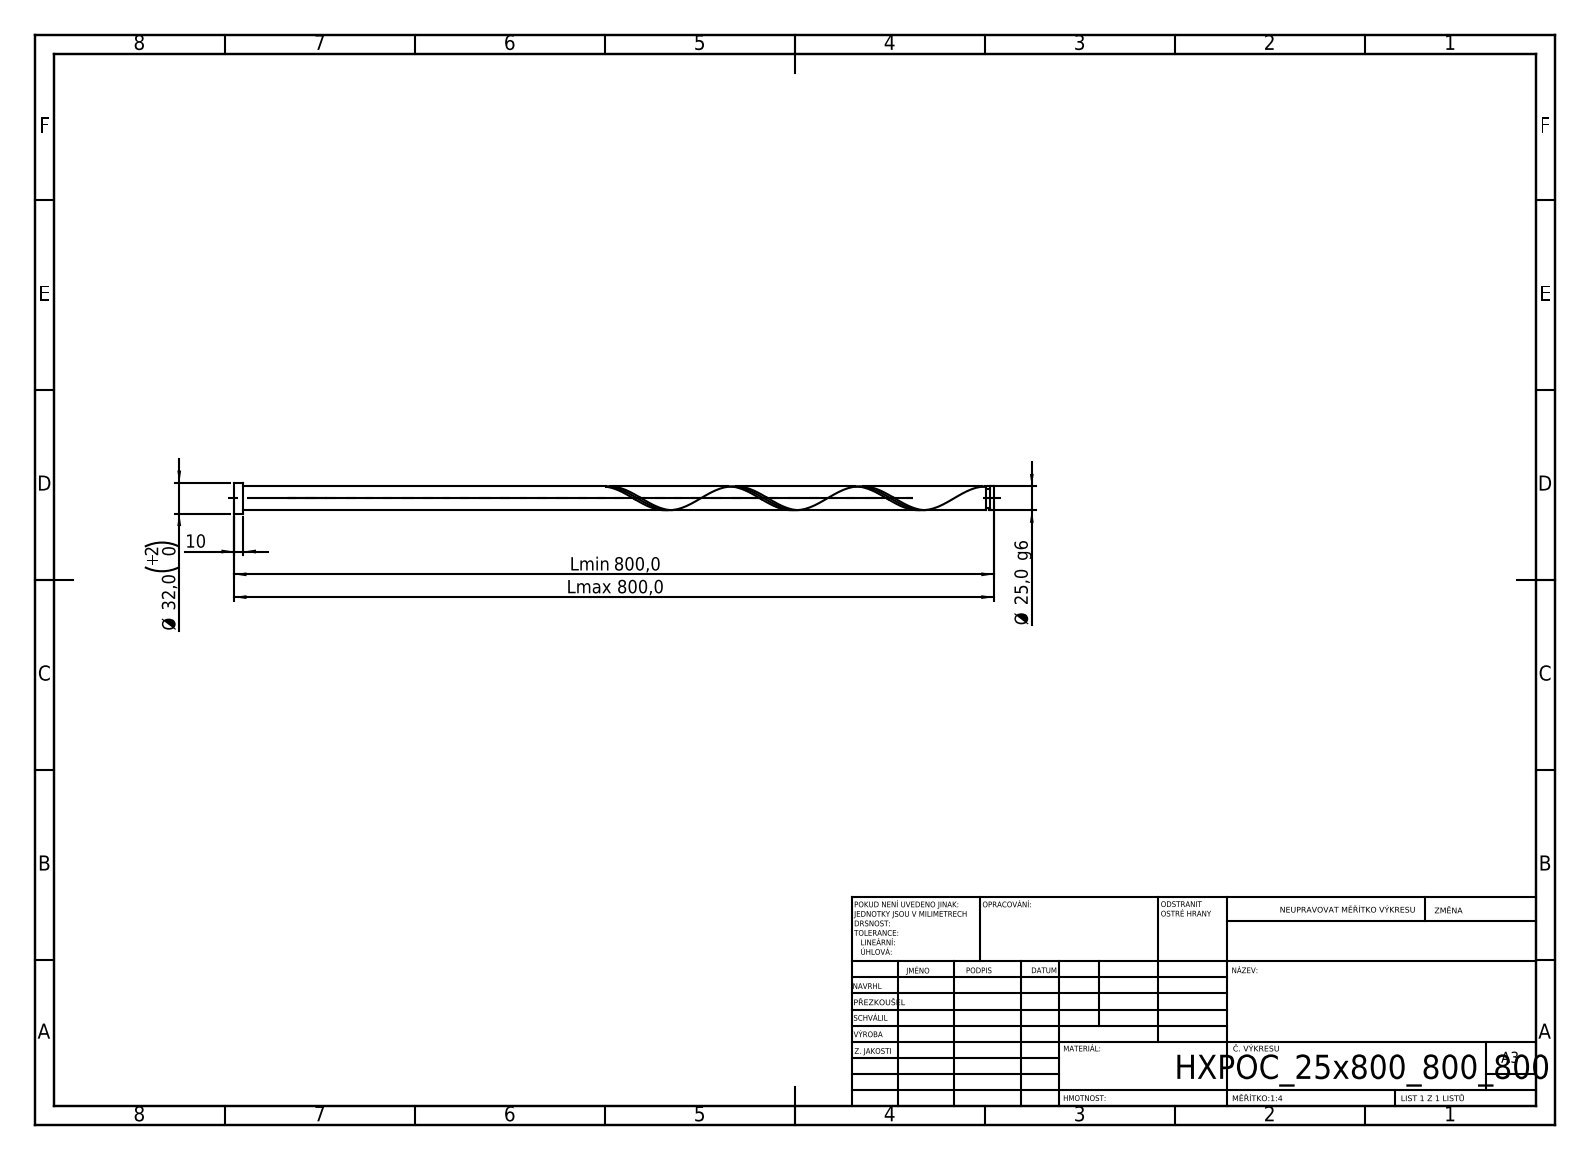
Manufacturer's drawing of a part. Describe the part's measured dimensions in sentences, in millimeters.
Its 3-D file was written by "SolidWorks 2019 (CONFIG_CONTROL_DESIGN)". It is 1 solid with 21 faces: 6 planar, 14 cylindrical and 1 other. Overall it measures 800 by 32 by 32 millimeters. Its volume is 391 190 cubic millimeters and its surface area 66 098 square millimeters. Round bosses or shafts: 1 of diameter 32, 1 of diameter 25, 1 of diameter 20. The main face-to-face distances are 800, 10, 790, 796.41, 786.41, 3.59, 791.41, 781.41, 5, 8.59.
